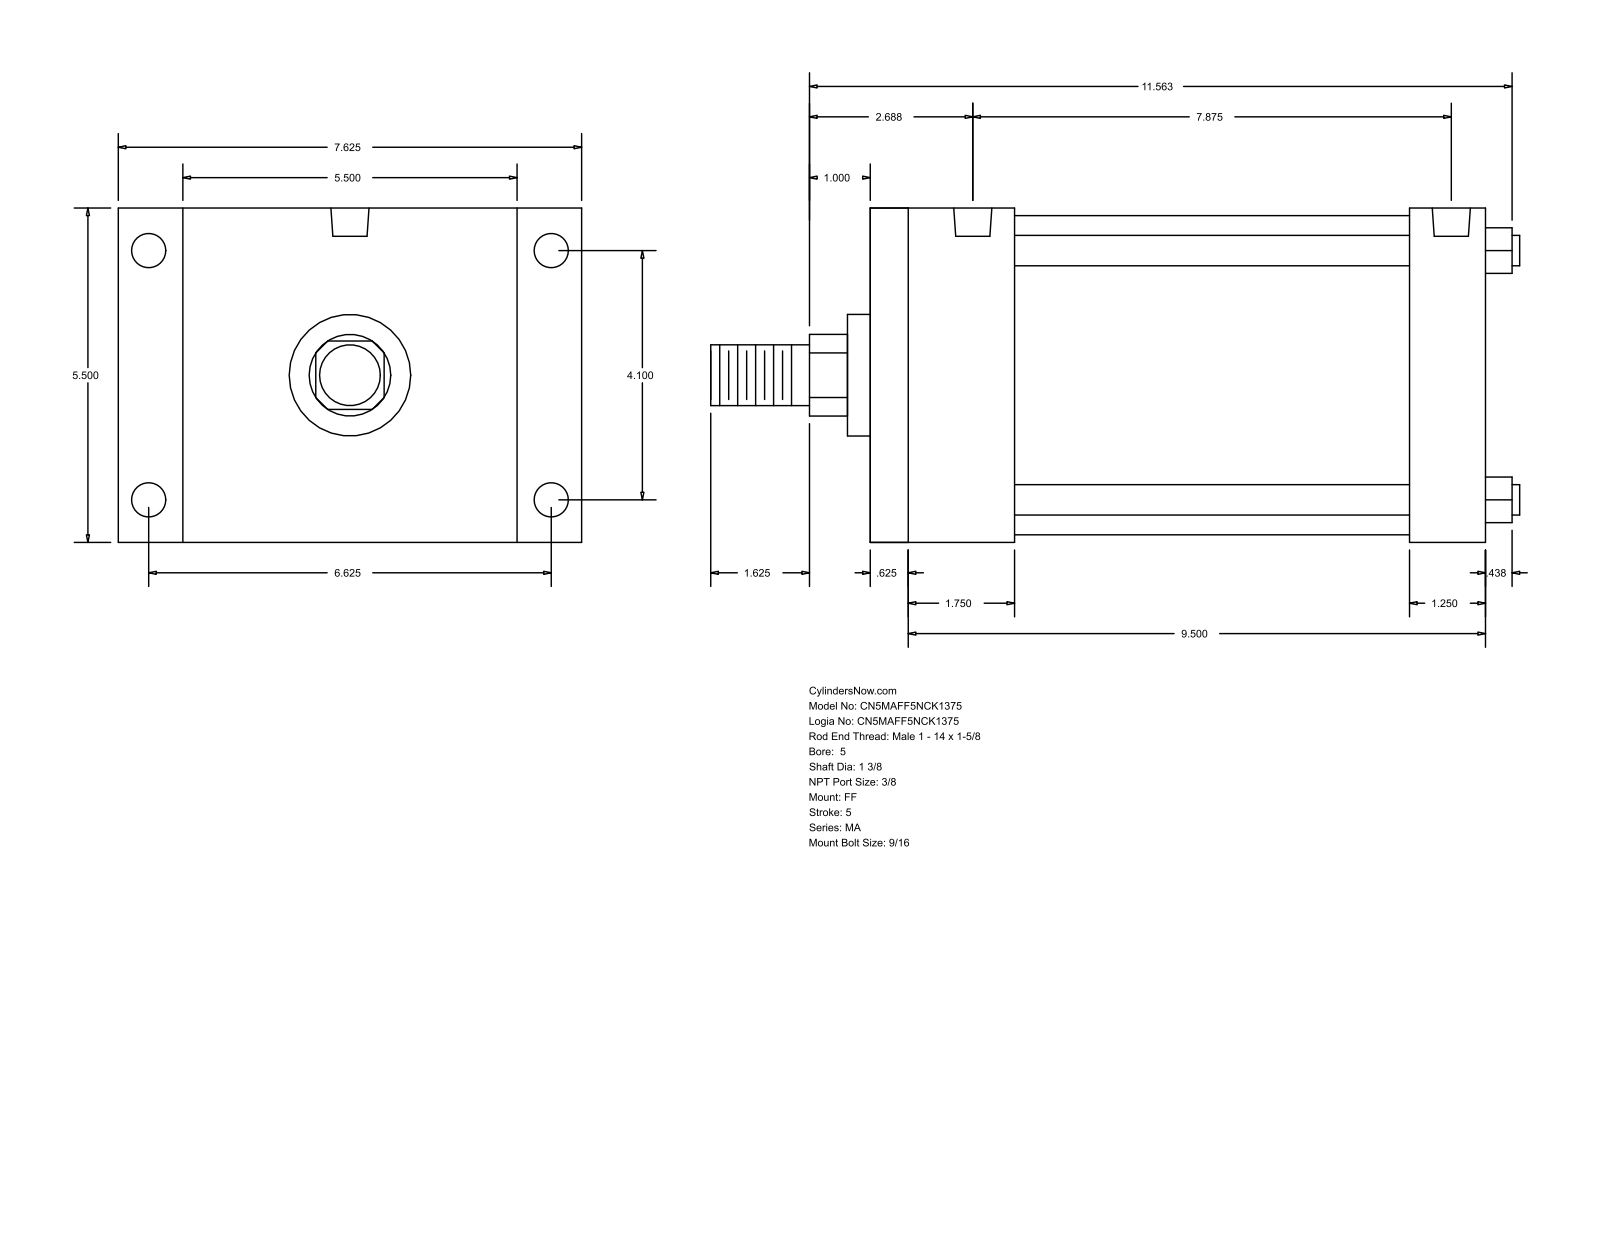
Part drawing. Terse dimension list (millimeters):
name: MA_FF__0500_1.375
written by: GSSL Pune (CONFIG_CONTROL_DESIGN)
unit: mm
bodies: 0 solids, 92 faces (64 planar, 28 cylindrical, 0 other)
size: 338.14 × 193.68 × 139.7
holes: 4× ⌀11.11, 4× ⌀14.29, 2× ⌀15.93
bosses: 4× ⌀12.7, 1× ⌀133.35, 1× ⌀50.8, 1× ⌀34.92, 1× ⌀25.4
rounds: 1× R17.06
face distances: 139.7, 257.17, 15.87, 241.3, 225.42, 209.55, 31.75, 60.32, 44.45, 165.1
hole spacings: 4.77, 104.14, 168.28, 190.49, 195.26, 197.9, 200.03
